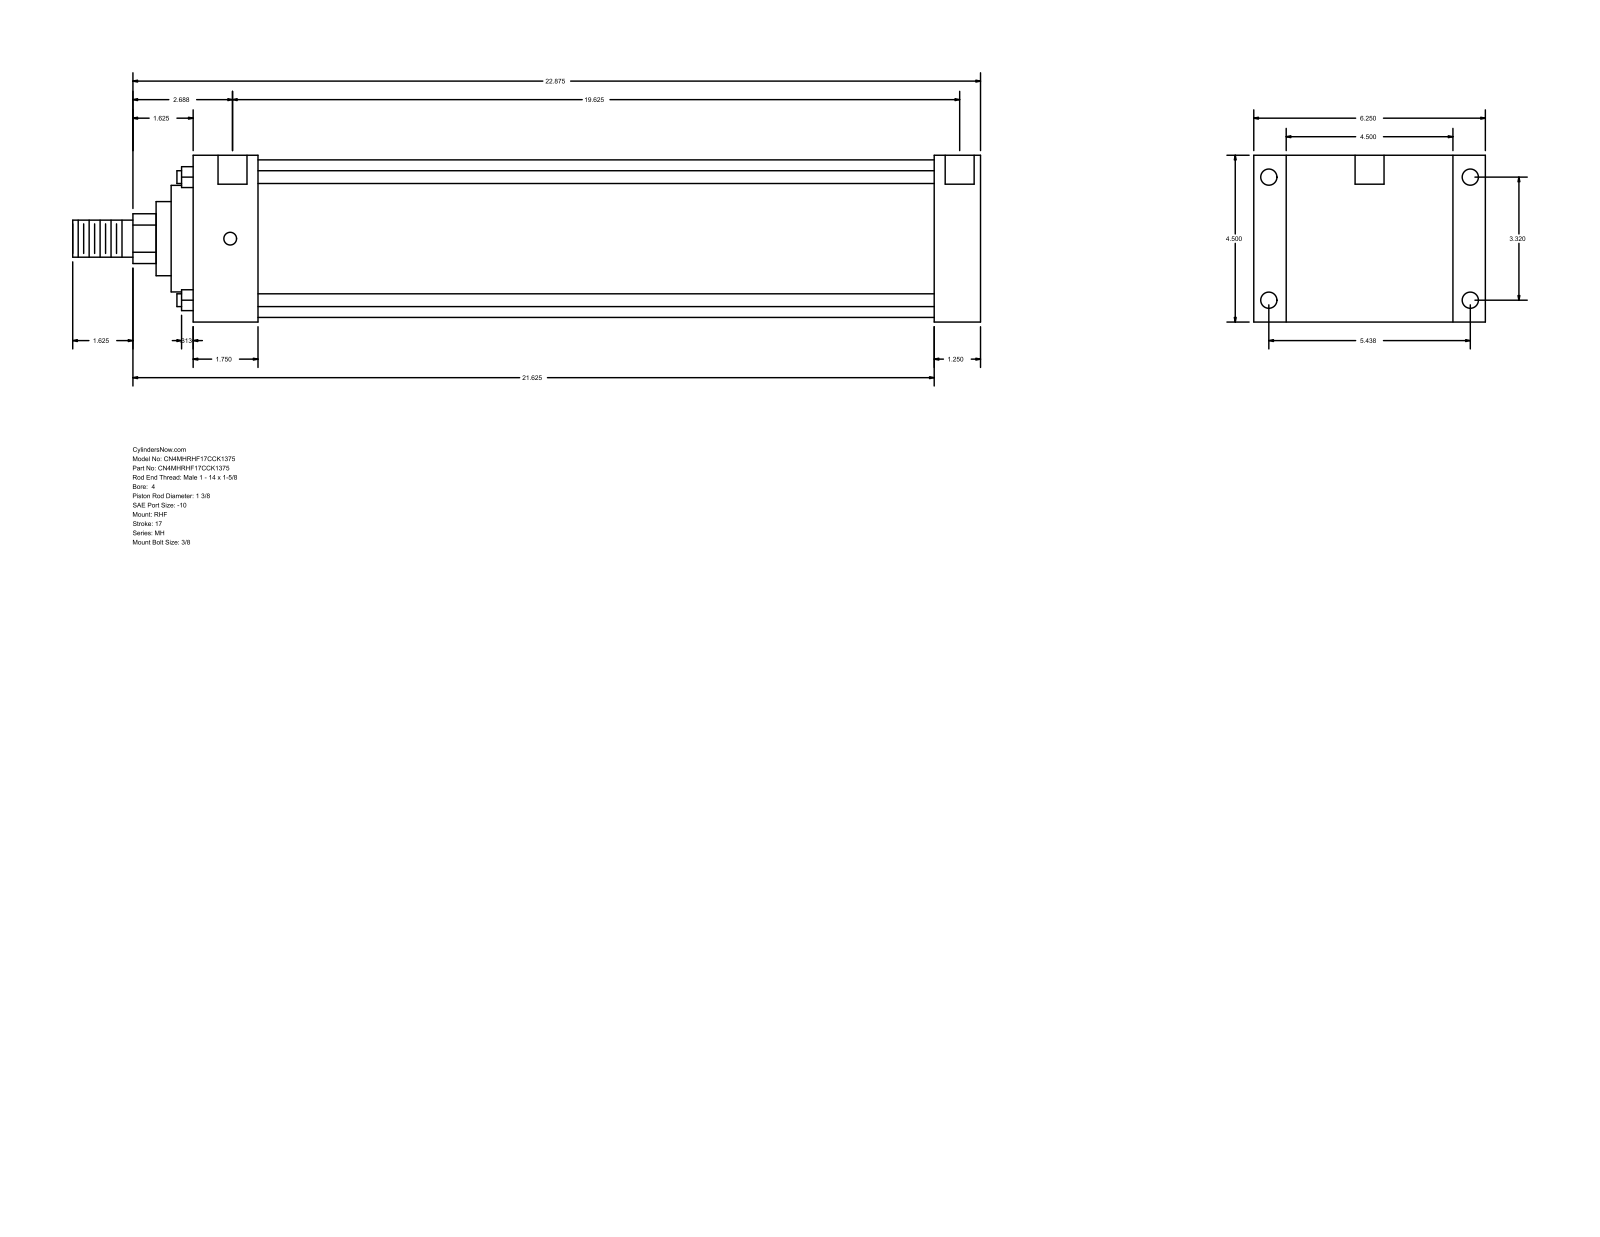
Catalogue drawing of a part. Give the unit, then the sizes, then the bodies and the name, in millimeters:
Units: millimetres
Overall size (bounding box): 622.3 × 158.75 × 114.3
Round holes (diameter × count): ⌀8.73 ×4, ⌀11.13 ×4, ⌀19.84 ×2
Round bosses / shafts (diameter × count): ⌀8.76 ×4, ⌀107.95 ×1, ⌀73.03 ×1, ⌀50.8 ×1, ⌀34.92 ×1, ⌀25.4 ×1
Partial cylindrical surfaces — rounded edges, fillets, slot ends (radius × count): R17.06 ×1
Main face-to-face distances: 114.3, 31.75, 508, 539.75, 22.23, 136.53, 44.45, 463.55, 495.3, 158.76
Hole centre spacings: 1.59, 84.32, 138.12, 161.82, 500.07, 501.66, 498.48
Bodies: 0 solids, 90 faces (61 planar, 29 cylindrical, 0 other)
Part name (STEP PRODUCT): MH_RHF__0400_1.375
STEP written by: GSSL Pune (CONFIG_CONTROL_DESIGN)
